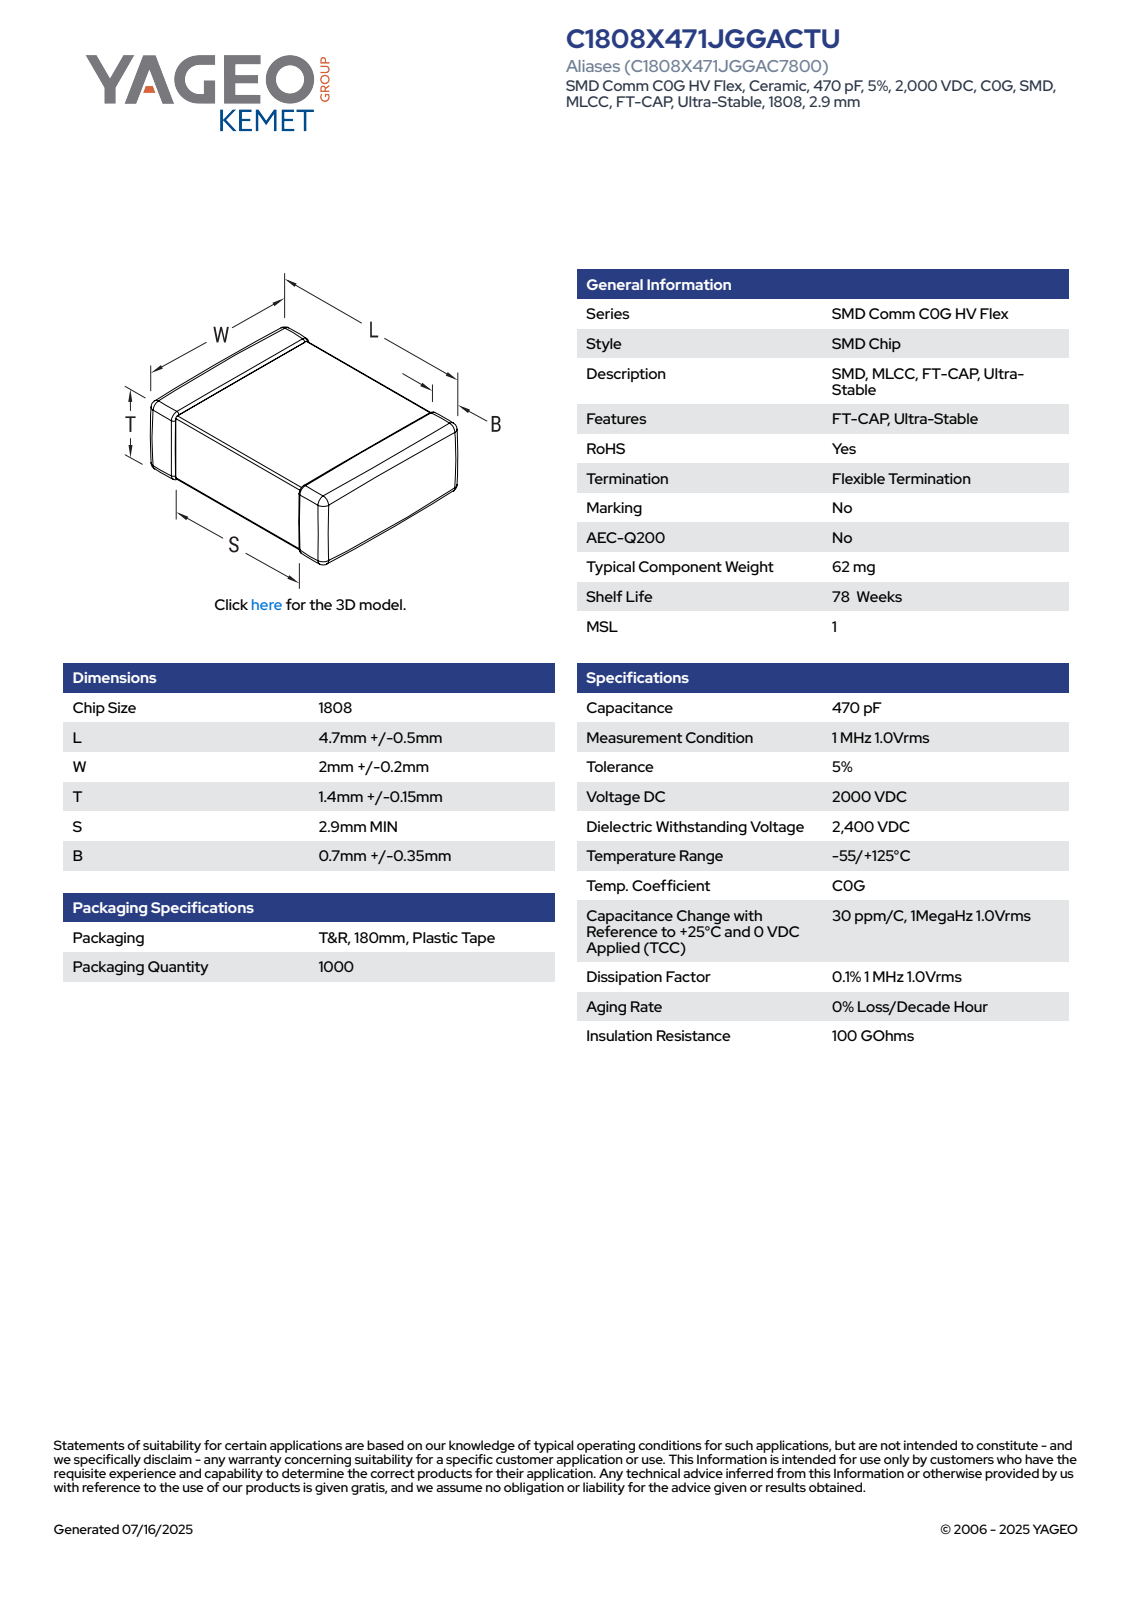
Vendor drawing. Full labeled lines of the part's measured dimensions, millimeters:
Part name (STEP PRODUCT): CCS_CCSTD_1808_L5.2W2.2T1.55B0.7
STEP written by: SolidWorks 2021 (AUTOMOTIVE_DESIGN)
Units: millimetres
Bodies: 4 solids, 129 faces (71 planar, 42 cylindrical, 16 other)
Overall size (bounding box): 5.2 × 2.2 × 1.55
Volume: 17 mm³ · Surface area: 45 mm²
Main face-to-face distances: 1.5, 1.45, 2.15, 2.1, 1.55, 5.2, 2.2, 1.51, 1.46, 0.33
